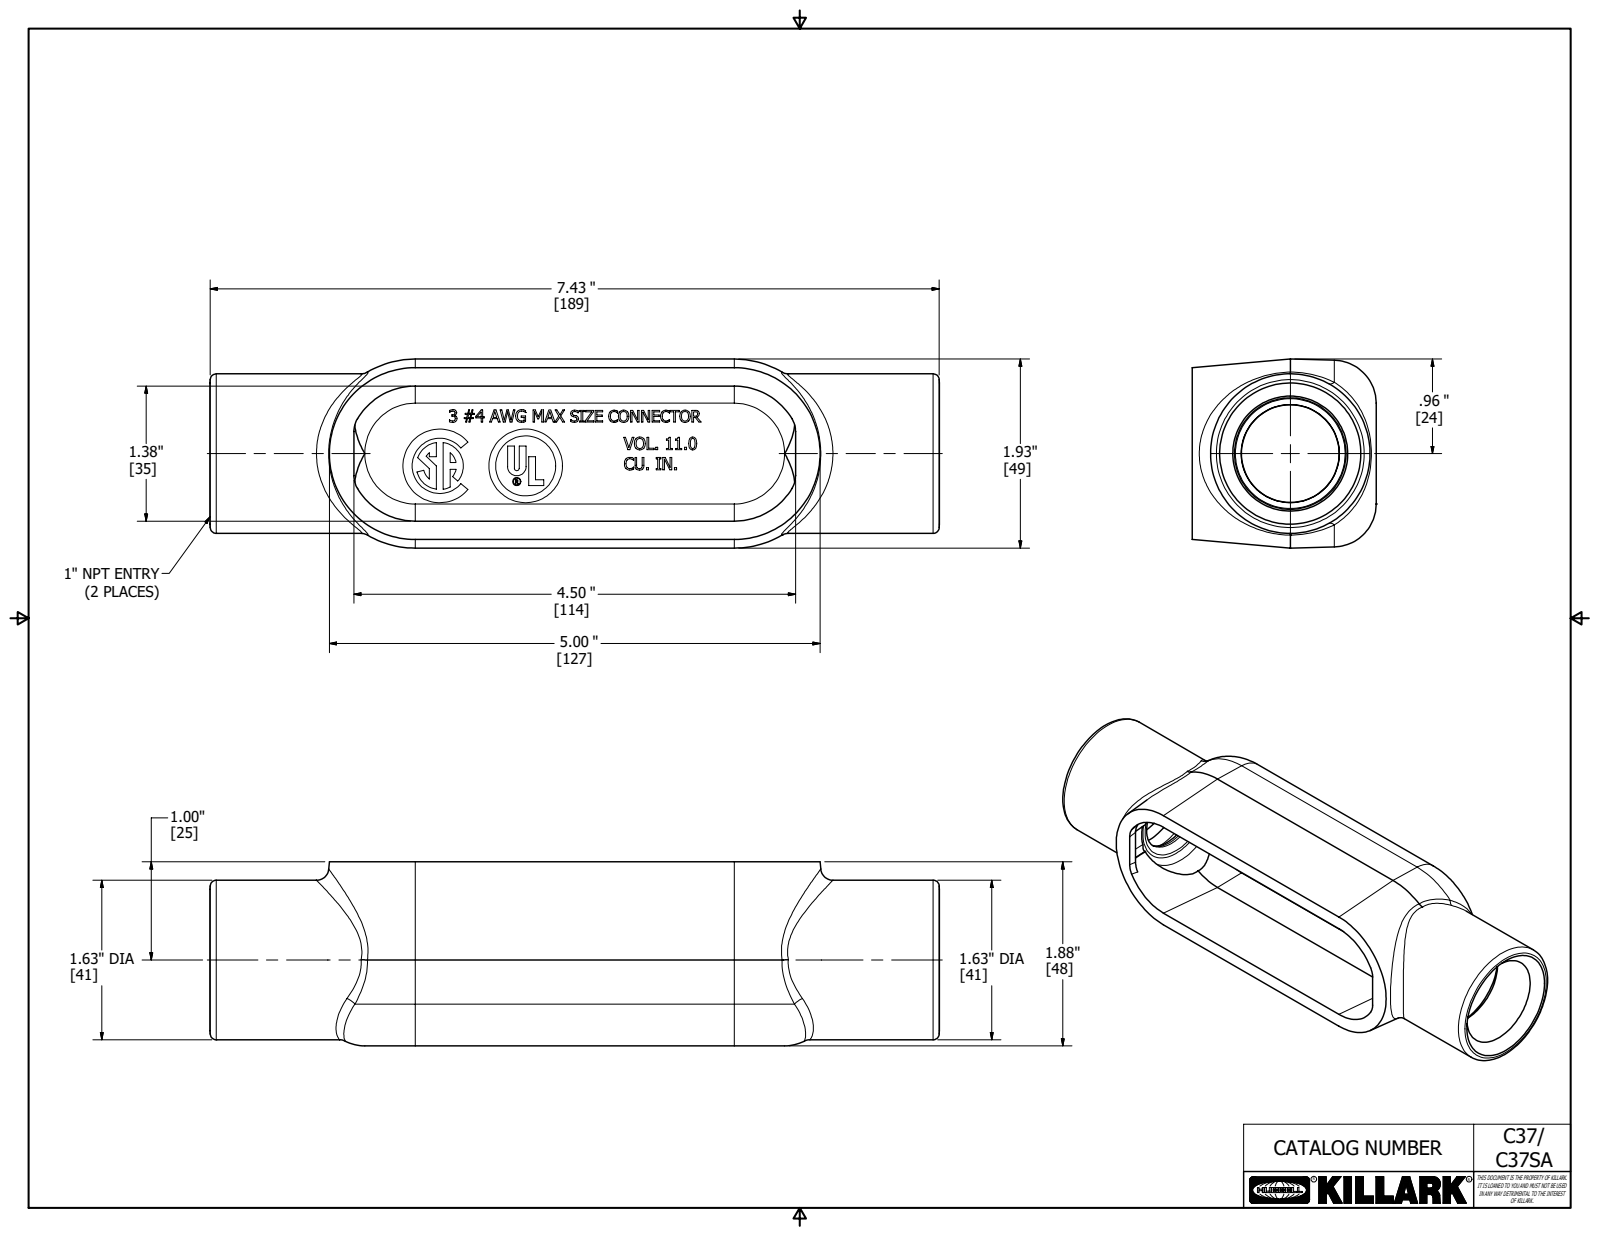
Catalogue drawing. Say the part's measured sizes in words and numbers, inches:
The part is named "17667-2". Its 3-D file was written by "Autodesk Inventor 2018 (AUTOMOTIVE_DESIGN)". It is 1 solid with 818 faces: 518 planar, 36 cylindrical and 264 other. Overall it measures 7.432 by 1.925 by 1.875 inches. Its volume is 7.012 cubic inches and its surface area 78.52 square inches. Round holes: 1 of diameter 0.07, 1 of diameter 0.611, 1 of diameter 1.321, 1 of diameter 1.375. Round bosses or shafts: 1 of diameter 1.625, 1 of diameter 0.75, 1 of diameter 0.083. Partial cylindrical surfaces (rounded edges, fillets, slot ends): 4 of radius 0.062, 4 of radius 0.125, 2 of radius 0.25, 2 of radius 0.437, 1 of radius 0.008, 1 of radius 0.013, 1 of radius 0.024, 1 of radius 0.094. The main face-to-face distances are 0.187, 0.187, 0.188, 1.875, 1.687, 0.031, 0.219, 1.656, 0.156, 1.844. The hole center spacings are 0.183.
